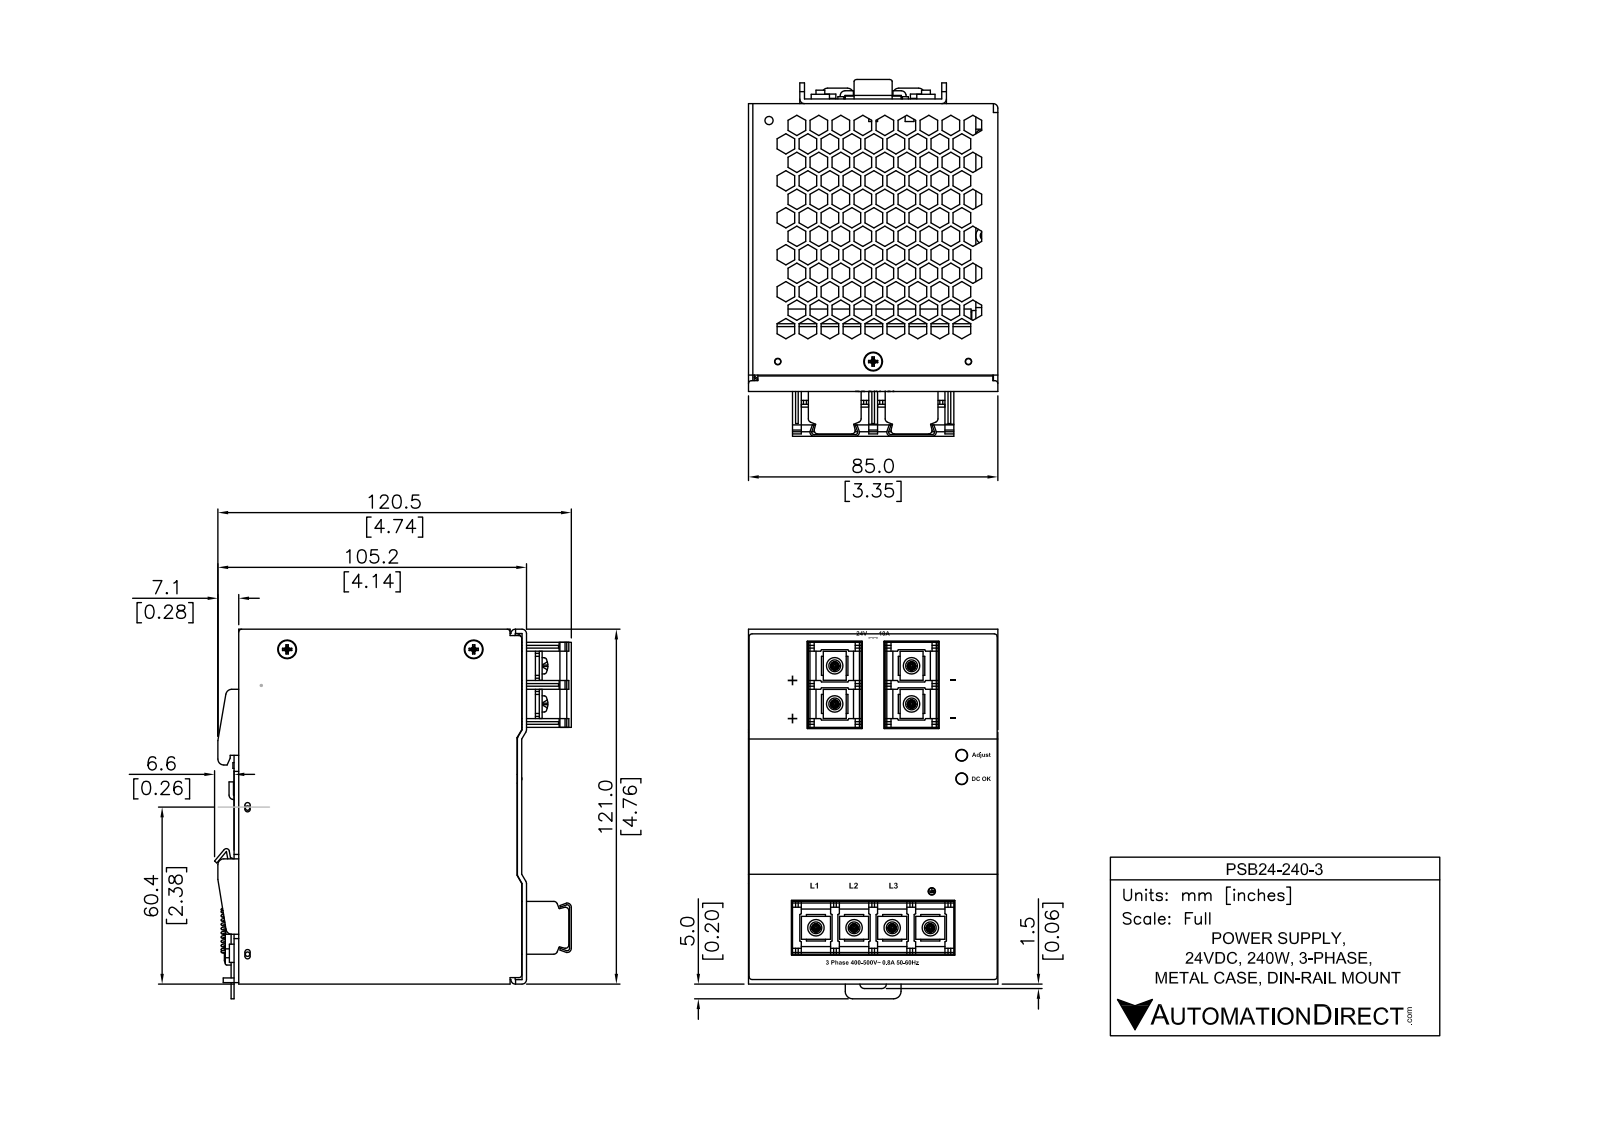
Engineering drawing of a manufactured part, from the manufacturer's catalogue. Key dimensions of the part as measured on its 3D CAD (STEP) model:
Part name (STEP PRODUCT): PSB24-240-3
STEP written by: SolidWorks 2011 (CONFIG_CONTROL_DESIGN)
Units: inches
Bodies: 2 solids, 2003 faces (1817 planar, 103 cylindrical, 83 other)
Overall size (bounding box): 4.946 × 4.612 × 3.35
Volume: 46.47 in³ · Surface area: 269.6 in²
Round holes (diameter × count): ⌀0.145 ×2
Round bosses / shafts (diameter × count): ⌀0.23 ×4, ⌀0.205 ×4, ⌀0.125 ×4
Partial cylindrical surfaces — rounded edges, fillets, slot ends (radius × count): R0.06 ×22, R0.03 ×12, R0.05 ×8, R0.04 ×3, R0.04 ×2, R0.075 ×2, R0.13 ×2, R0.01 ×1
Main face-to-face distances: 0.073, 3.273, 0.443, 2.903, 0.37, 2.83, 0.075, 3.346, 3.2, 2.46
Hole centre spacings: 0.3
